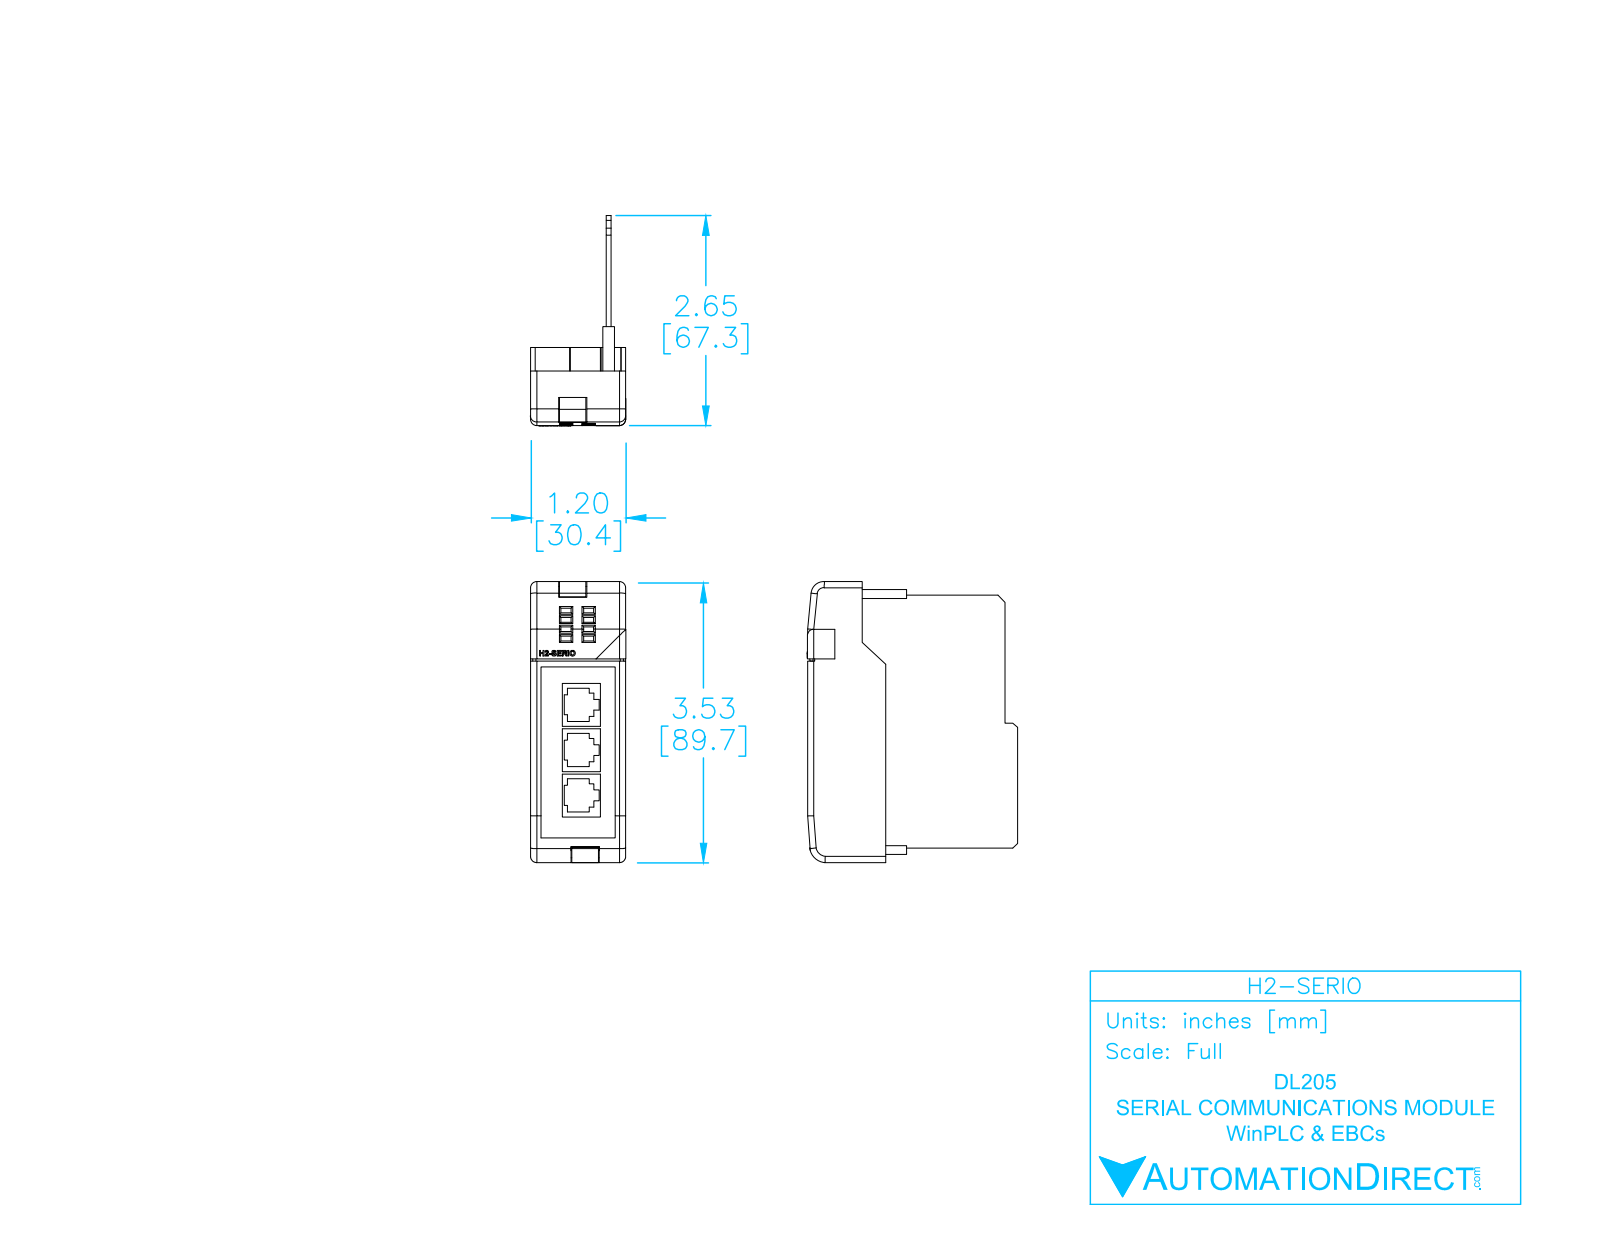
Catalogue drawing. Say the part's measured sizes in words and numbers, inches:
The part is named "H2-SERIO". Its 3-D file was written by "SolidWorks 2009 (AUTOMOTIVE_DESIGN)". It is 5 solids with 435 faces: 301 planar, 84 cylindrical and 50 other. Overall it measures 3.543 by 2.653 by 1.203 inches. Its volume is 1.246 cubic inches and its surface area 48.83 square inches. Partial cylindrical surfaces (rounded edges, fillets, slot ends): 28 of radius 0.02, 11 of radius 0.079, 4 of radius 0.01, 2 of radius 0.039, 1 of radius 0.103, 1 of radius 0.149, 1 of radius 0.162, 1 of radius 0.208. The main face-to-face distances are 0.059, 0.186, 1.142, 0.127, 0.245, 0.956, 0.02, 0.571, 1.083, 0.039.
